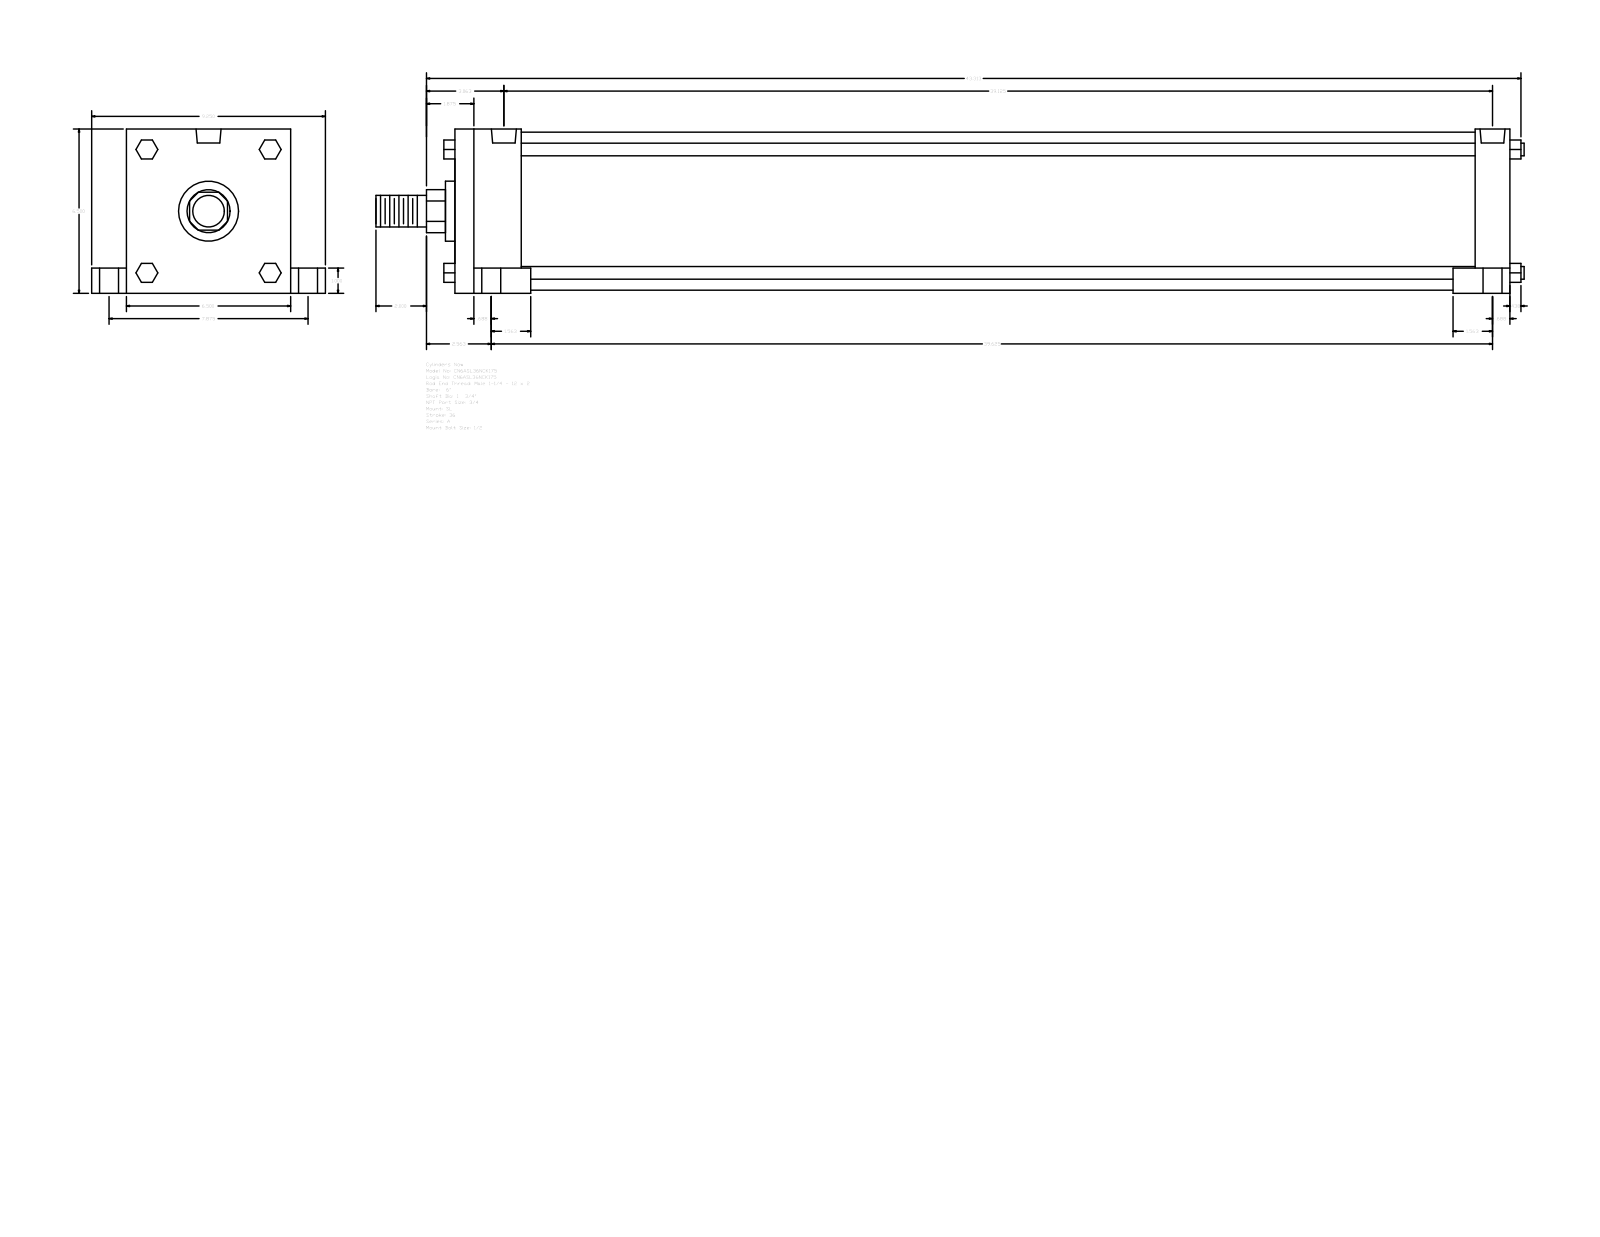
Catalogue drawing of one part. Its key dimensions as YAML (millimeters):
part_name: "A_SL__0600_1.75"
step_written_by: "GSSL Pune (CONFIG_CONTROL_DESIGN)"
units: millimeters
bodies: {solids: 0, faces: 150, planar: 114, cylindrical: 36, other: 0}
overall_size: [1154.11, 234.95, 165.1]
round_holes:
  - {diameter: 15.08, count: 4}
  - {diameter: 19.05, count: 4}
  - {diameter: 25.4, count: 4}
  - {diameter: 25.12, count: 2}
round_bosses_or_shafts:
  - {diameter: 12.7, count: 4}
  - {diameter: 158.75, count: 1}
  - {diameter: 60.33, count: 1}
  - {diameter: 44.45, count: 1}
  - {diameter: 31.75, count: 1}
partial_cylinders:
  - {radius: 21.63, count: 1}
face_to_face_distances: [165.1, 1060.46, 66.68, 993.78, 1025.53, 958.85, 34.93, 25.4, 139.7, 34.92]
hole_center_spacings: [5.56, 100.01, 100.16, 100.81, 101.66, 200.02, 982.65, 988.21]
